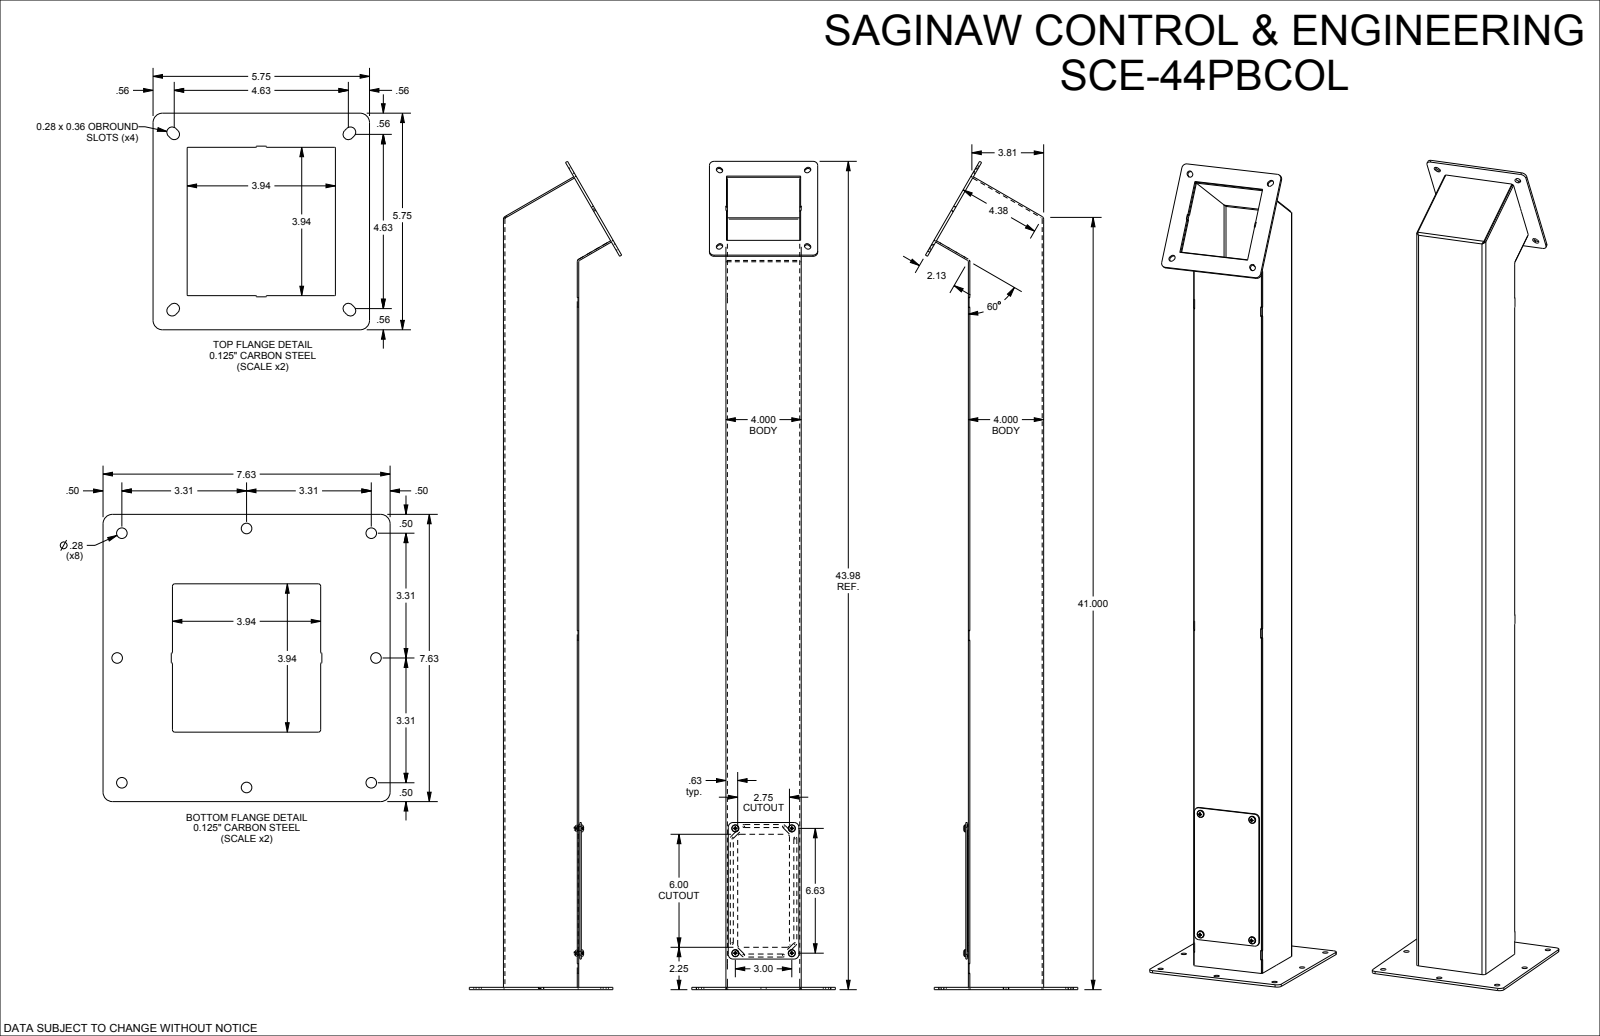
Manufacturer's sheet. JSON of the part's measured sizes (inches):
{"part_name": "SCE-44PBCOL", "step_written_by": "SolidWorks 2019 (AUTOMOTIVE_DESIGN)", "units": "inches", "bodies": {"solids": 14, "faces": 481, "planar": 205, "cylindrical": 152, "other": 124}, "overall_size": [43.976, 8.092, 7.625], "volume_in3": 51.56, "surface_area_in2": 1524, "round_holes": [[0.281, 8], [0.19, 4], [0.218, 4], [0.25, 4]], "round_bosses_or_shafts": [[0.373, 4], [0.34, 4], [0.249, 4], [0.188, 4]], "partial_cylinders_radius": [[0.015, 28], [0.01, 16], [0.25, 12], [0.08, 9], [0.045, 8], [0.141, 8], [0.205, 8], [0.096, 5]], "face_to_face_distances": [0.06, 3.94, 4, 3.88, 0.078, 3.922, 3.862, 0.125, 4.06, 0.138], "hole_center_spacings": [3.315, 7.519, 4.861, 6.625, 3, 6.625, 6.875, 7.272]}
